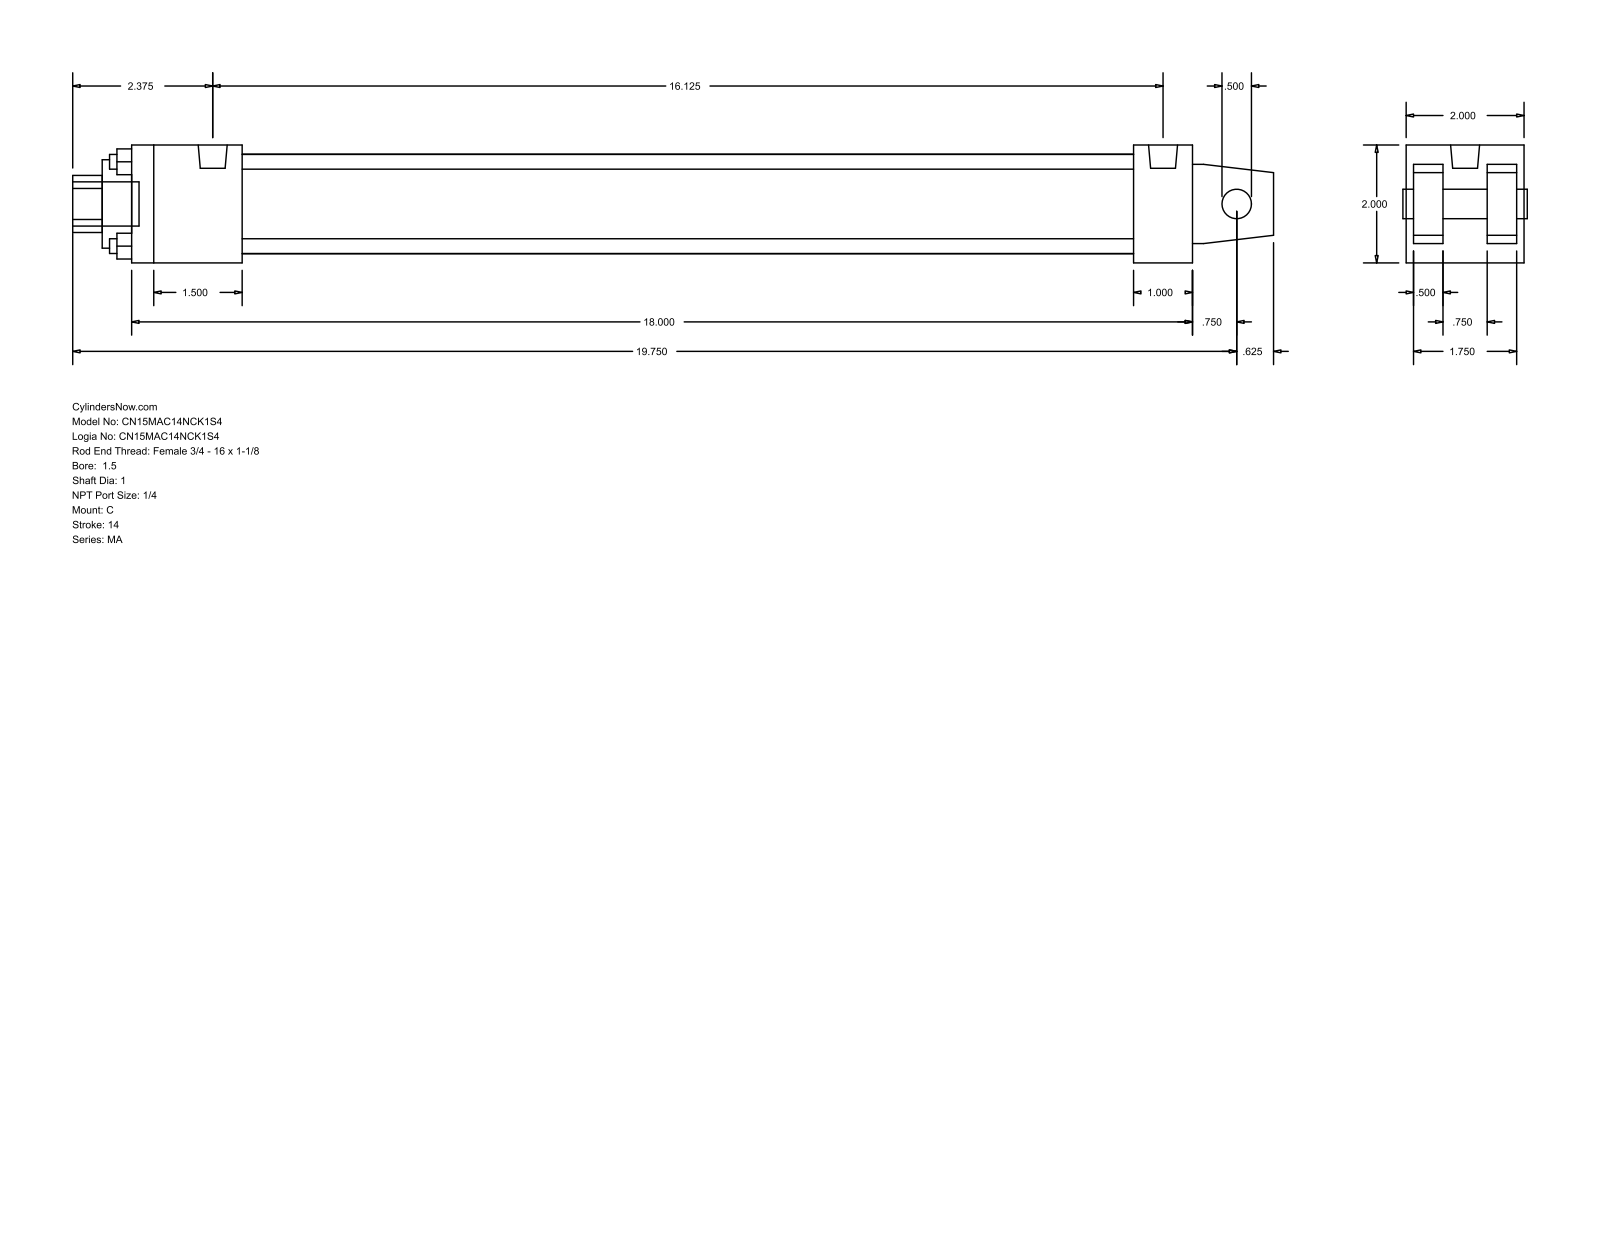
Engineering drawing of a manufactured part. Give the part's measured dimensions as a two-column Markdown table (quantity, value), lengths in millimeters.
| quantity | value |
| --- | --- |
| part name | MA_C__0150_1 |
| STEP written by | GSSL Pune (CONFIG_CONTROL_DESIGN) |
| units | millimeters |
| bodies | 0 solids, 103 faces (76 planar, 27 cylindrical, 0 other) |
| overall size | 517.52 × 50.8 × 50.8 |
| round holes (diameter × count) | 6.35 × 4, 12.7 × 1, 25.4 × 1, 38.1 × 1, 42.93 × 1 |
| round bosses / shafts (diameter × count) | 7.94 × 4, 12.49 × 2, 19.05 × 1 |
| partial cylindrical surfaces (radius × count) | 12.29 × 1 |
| main face-to-face distances | 50.8, 47.63, 12.7, 3.17, 15.87, 34.93, 31.76, 44.46, 457.2, 25.4 |
| hole center spacings | 25.68, 36.32, 51.36 |
